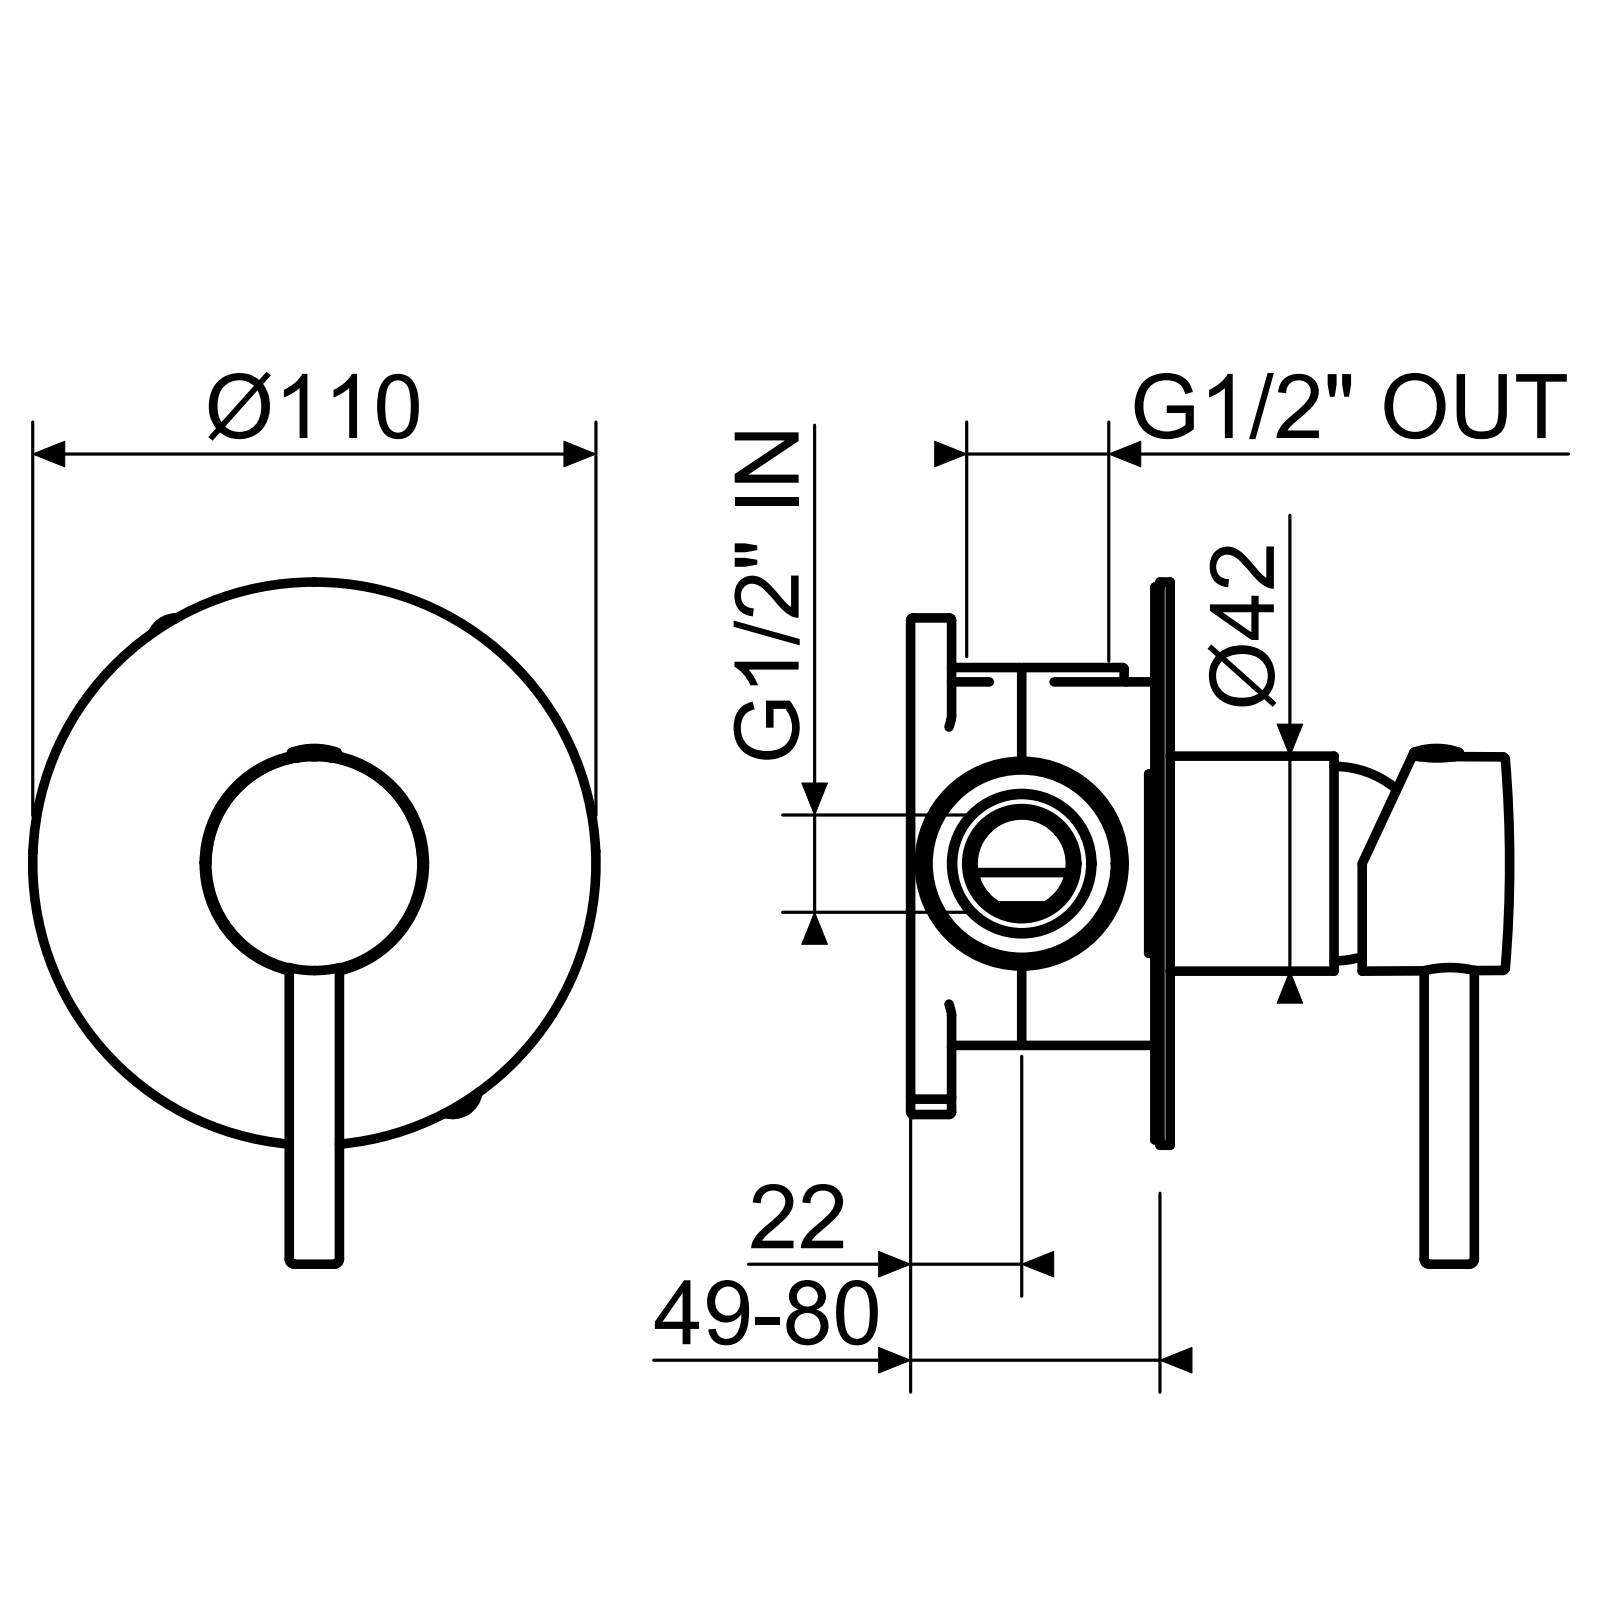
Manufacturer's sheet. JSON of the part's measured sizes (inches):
{"part_name": "SINMAC0008; SCCMAC0005; ALOG005C004; ALOG005C002 (+6 more)", "step_written_by": "CREO PARAMETRIC BY PTC INC, 2020281 (CONFIG_CONTROL_DESIGN)", "units": "inches", "bodies": {"solids": 7, "faces": 255, "planar": 68, "cylindrical": 89, "other": 98}, "overall_size": [5.177, 4.331, 2.776], "volume_in3": 2.227, "surface_area_in2": 71.31, "round_holes": [[0.315, 3], [0.165, 2], [0.197, 1], [0.201, 1], [0.256, 1], [1.142, 1], [1.289, 1], [1.358, 1], [1.575, 1], [1.693, 1], [1.713, 1], [1.831, 1]], "round_bosses_or_shafts": [[4.331, 1], [1.929, 1], [1.654, 1], [1.339, 1], [0.197, 1]], "partial_cylinders_radius": [[0.039, 14], [0.02, 11], [0.079, 4], [0.012, 2], [0.059, 2], [0.102, 2], [0.118, 2], [0.189, 2]], "face_to_face_distances": [0.079, 2.539, 2.618, 2.461, 0.157, 0.236, 2.697, 2.776, 0.039, 1.457], "hole_center_spacings": [0.453]}
